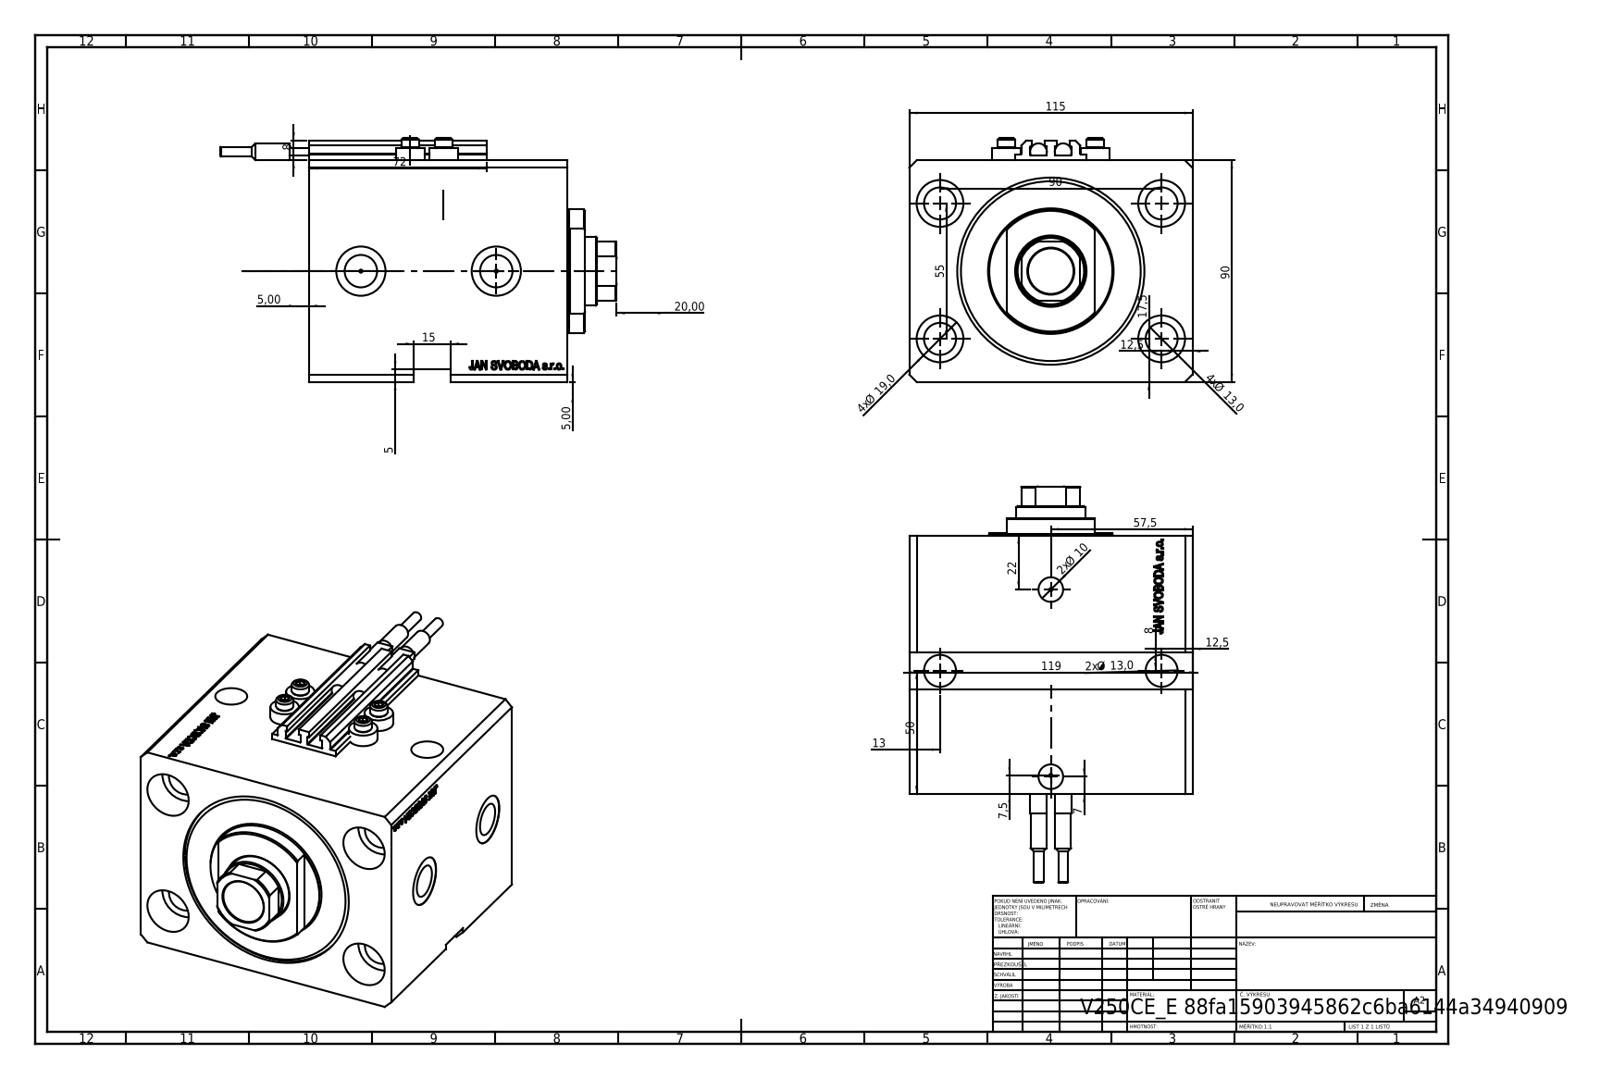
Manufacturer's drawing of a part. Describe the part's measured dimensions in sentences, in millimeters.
The part is named "V250CE_VC_E; SWITCH_V250CE; ALLEN BOLT V250CE; V250CE_E_Body (+1 more)". Its 3-D file was written by "SolidWorks 2019 (CONFIG_CONTROL_DESIGN)". It is 10 solids with 1175 faces: 579 planar, 150 cylindrical and 446 other. Overall it measures 160.9 by 115 by 99 millimeters. Its volume is 954 473 cubic millimeters and its surface area 160 400 square millimeters. Round holes: 6 of diameter 13, 4 of diameter 1.25, 4 of diameter 4, 4 of diameter 19, 2 of diameter 10, 2 of diameter 13.16, 2 of diameter 20, 1 of diameter 18.5, 1 of diameter 28, 1 of diameter 63, 1 of diameter 76. Round bosses or shafts: 4 of diameter 11.6, 4 of diameter 7, 2 of diameter 6.8, 2 of diameter 6.5, 2 of diameter 4, 1 of diameter 50. Partial cylindrical surfaces (rounded edges, fillets, slot ends): 10 of radius 0.2, 1 of radius 13.5. The main face-to-face distances are 90, 115, 105, 87.1, 17.9, 57, 74.9, 30.1, 20, 54.9. The hole center spacings are 52.74, 55, 90, 13.6, 27.39, 28.46, 33.62, 36.
